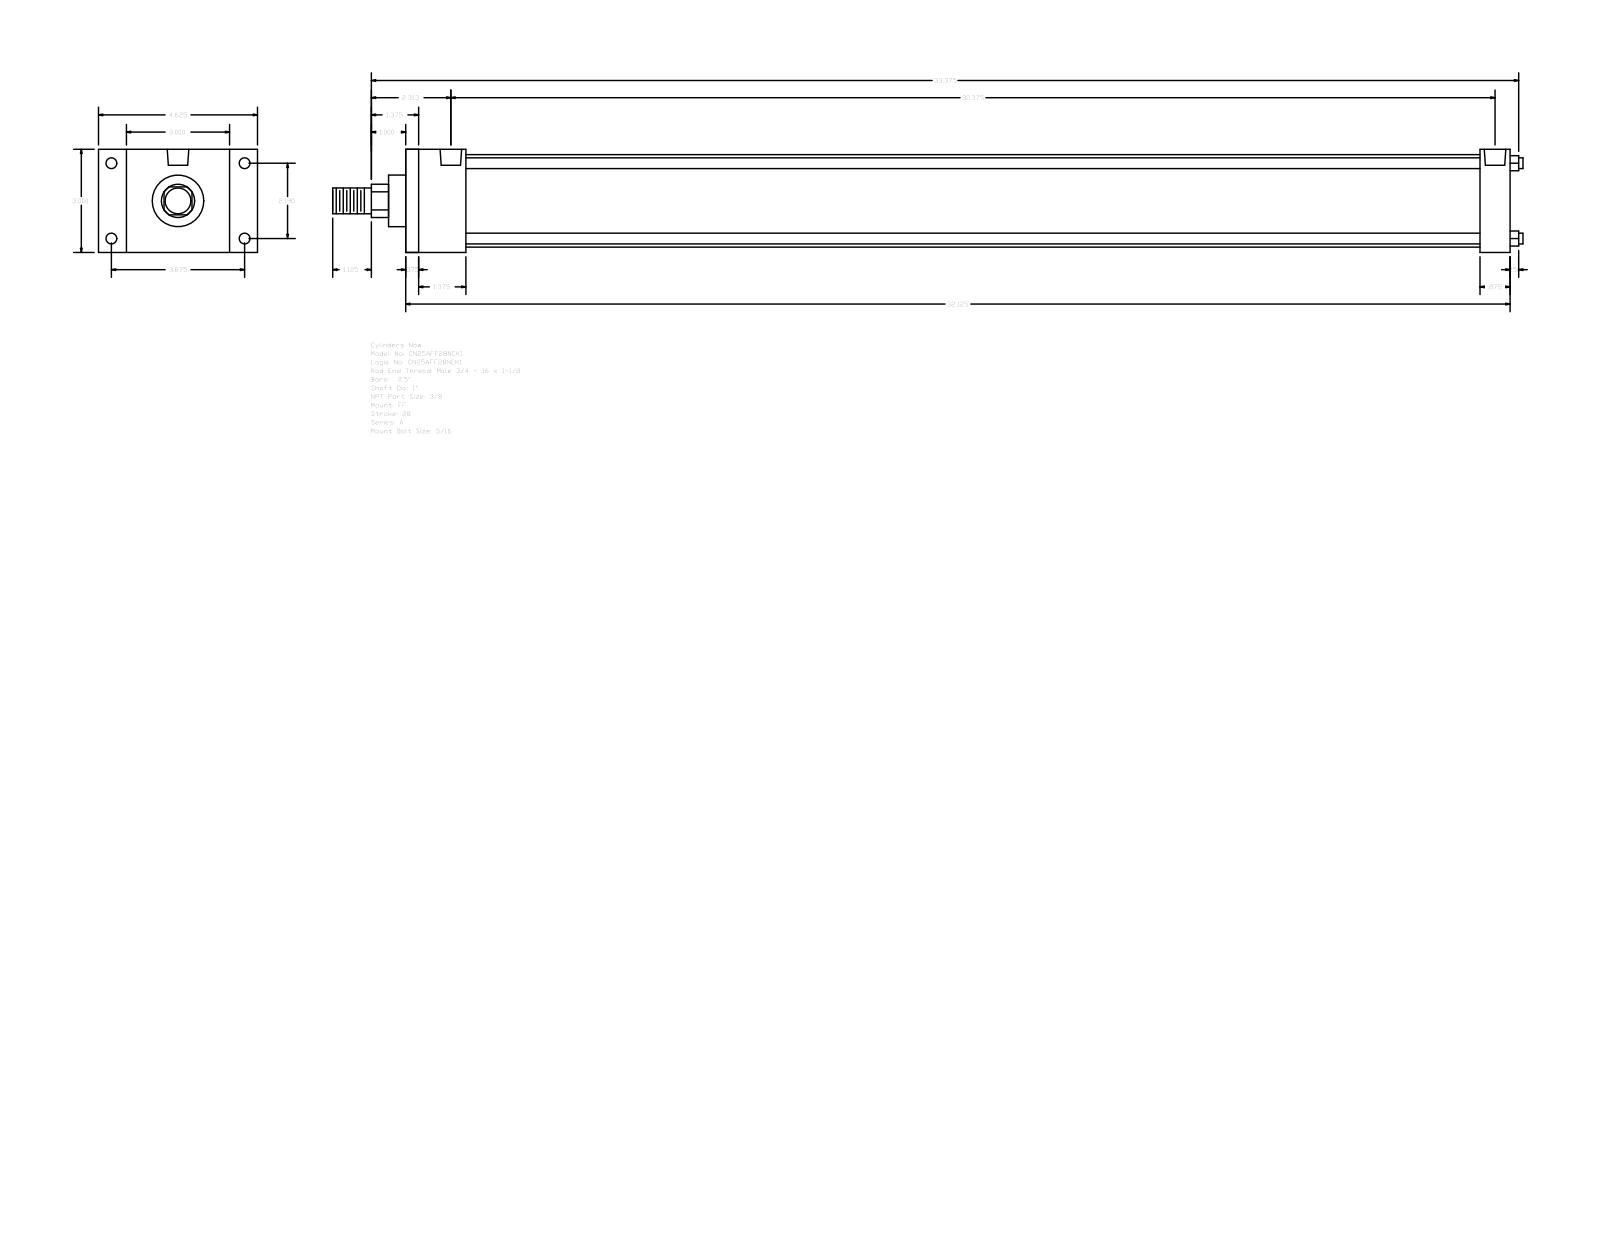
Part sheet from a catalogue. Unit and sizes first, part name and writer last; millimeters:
Units: millimetres
Overall size (bounding box): 879.48 × 117.47 × 76.2
Round holes (diameter × count): ⌀5.56 ×4, ⌀7.94 ×4, ⌀15.93 ×2
Round bosses / shafts (diameter × count): ⌀7.94 ×4, ⌀68.33 ×1, ⌀38.1 ×1, ⌀25.4 ×1, ⌀19.05 ×1
Partial cylindrical surfaces — rounded edges, fillets, slot ends (radius × count): R12.29 ×1
Main face-to-face distances: 76.2, 815.98, 9.52, 806.46, 44.45, 793.75, 34.93, 784.23, 749.3, 771.53
Hole centre spacings: 2.38, 55.62, 98.42, 113.05, 773.9, 776.28, 771.52
Bodies: 0 solids, 92 faces (64 planar, 28 cylindrical, 0 other)
Part name (STEP PRODUCT): A_FF__0250_1
STEP written by: GSSL Pune (CONFIG_CONTROL_DESIGN)
